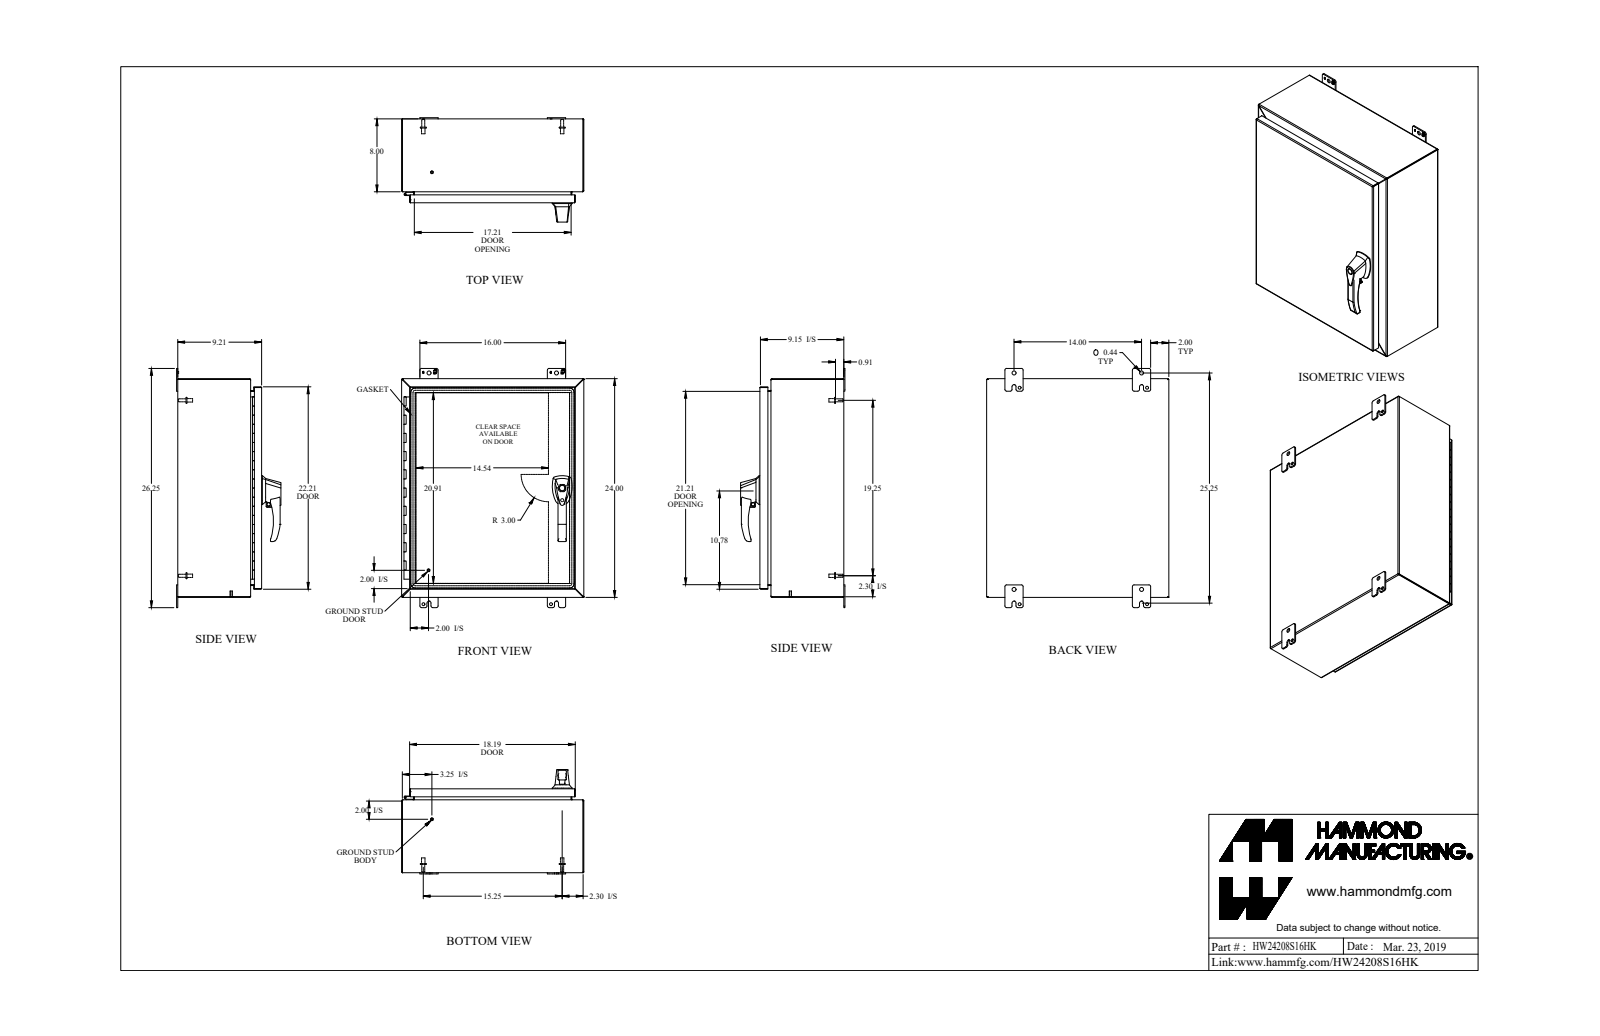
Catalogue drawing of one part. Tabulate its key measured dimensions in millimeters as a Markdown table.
| quantity | value |
| --- | --- |
| part name | HW24208S16HK |
| STEP written by | SolidWorks 2018 (AUTOMOTIVE_DESIGN) |
| units | millimeters |
| bodies | 46 solids, 1420 faces (688 planar, 580 cylindrical, 152 other) |
| overall size | 666.8 × 508 × 290.8 |
| volume | 2 712 000 mm³ |
| surface area | 2 725 000 mm² |
| round holes (diameter × count) | 4.5 × 6, 8 × 5, 6.4 × 3, 6.7 × 3, 10.5 × 3, 5 × 2, 6.5 × 2, 10 × 2, 11.1 × 2, 2.8 × 1, 5.9 × 1, 8.4 × 1 |
| round bosses / shafts (diameter × count) | 9.5 × 9, 6.4 × 7, 4 × 6, 16.5 × 4, 8.4 × 4, 8 × 4, 25.4 × 3, 13 × 3 |
| partial cylindrical surfaces (radius × count) | 6.4 × 27, 4.8 × 24, 0.9 × 20, 2.7 × 20, 1.5 × 12, 3.2 × 9, 1.1 × 8, 5.5 × 8 |
| main face-to-face distances | 1.8, 232.1, 230.3, 1.8, 232.1, 233.9, 506.2, 607.8, 201.4, 504.3 |
| hole center spacings | 28.2, 206.2, 206.2, 412.4, 34, 172.2, 192.4, 192.5 |
